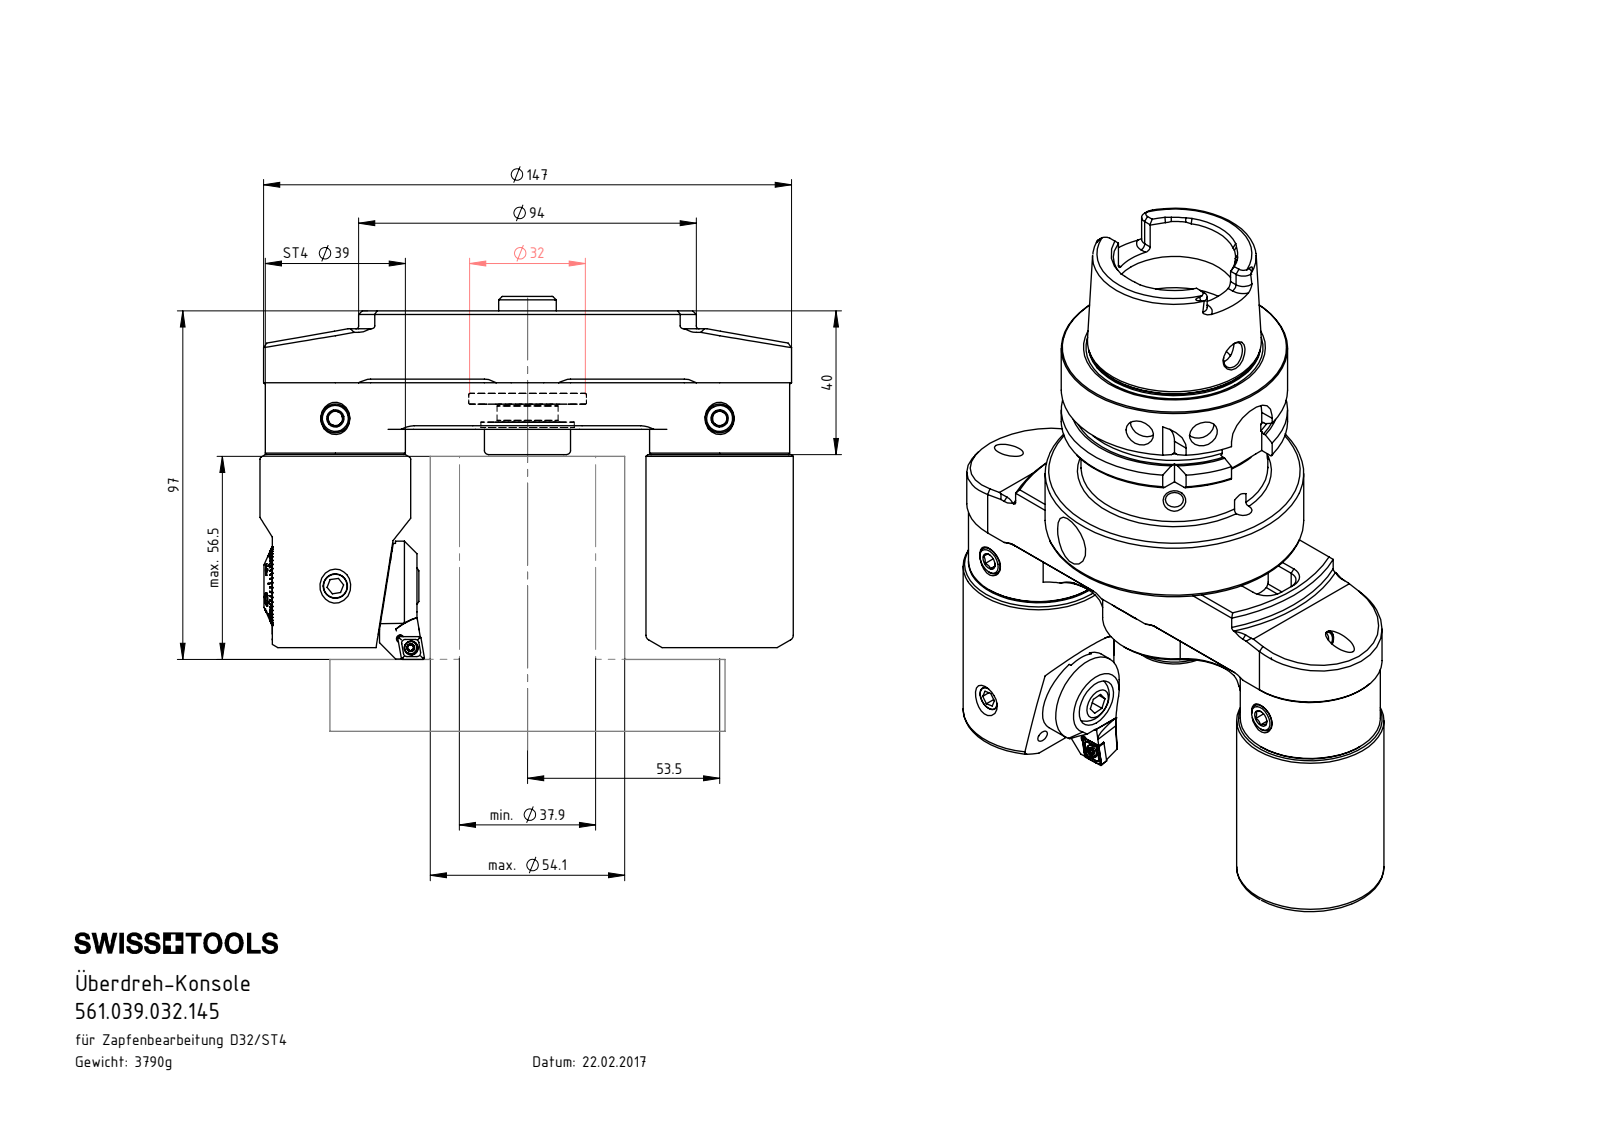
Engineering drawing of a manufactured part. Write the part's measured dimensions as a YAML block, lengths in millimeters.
part_name: "A42-BG2.012.005_A; F42-BG1.011.027_C; CWF-ST4.041.053; ST4-F42.K21.057_max mit WP Halter Standart (+8 more)"
step_written_by: "SolidWorks 2017 (CONFIG_CONTROL_DESIGN)"
units: millimeters
bodies: {solids: 35, faces: 1735, planar: 559, cylindrical: 412, other: 764}
overall_size: [188.9, 148.5, 72]
volume: 473539
surface_area: 120835
round_holes:
  - {diameter: 5, count: 13}
  - {diameter: 3.5, count: 4}
  - {diameter: 4, count: 4}
  - {diameter: 3.3, count: 3}
  - {diameter: 8, count: 3}
  - {diameter: 22, count: 3}
  - {diameter: 2.5, count: 2}
  - {diameter: 3, count: 2}
  - {diameter: 4.2, count: 2}
  - {diameter: 6.8, count: 2}
  - {diameter: 7.25, count: 2}
  - {diameter: 8.5, count: 2}
round_bosses_or_shafts:
  - {diameter: 8, count: 4}
  - {diameter: 21.8, count: 3}
  - {diameter: 39, count: 2}
  - {diameter: 21.3, count: 2}
  - {diameter: 14, count: 2}
  - {diameter: 6, count: 2}
  - {diameter: 5, count: 2}
  - {diameter: 4.6, count: 2}
partial_cylinders:
  - {radius: 0.5, count: 12}
  - {radius: 3.2, count: 7}
  - {radius: 0.21, count: 6}
  - {radius: 1.4, count: 6}
  - {radius: 0.36, count: 5}
  - {radius: 0.8, count: 5}
  - {radius: 2.88, count: 4}
  - {radius: 3.48, count: 4}
face_to_face_distances: [40, 7, 13, 20, 16, 10, 18, 58, 53.75, 93.75]
hole_center_spacings: [107, 13.2, 0.35, 12.25, 13.3, 16.87, 17.05, 20.28]
